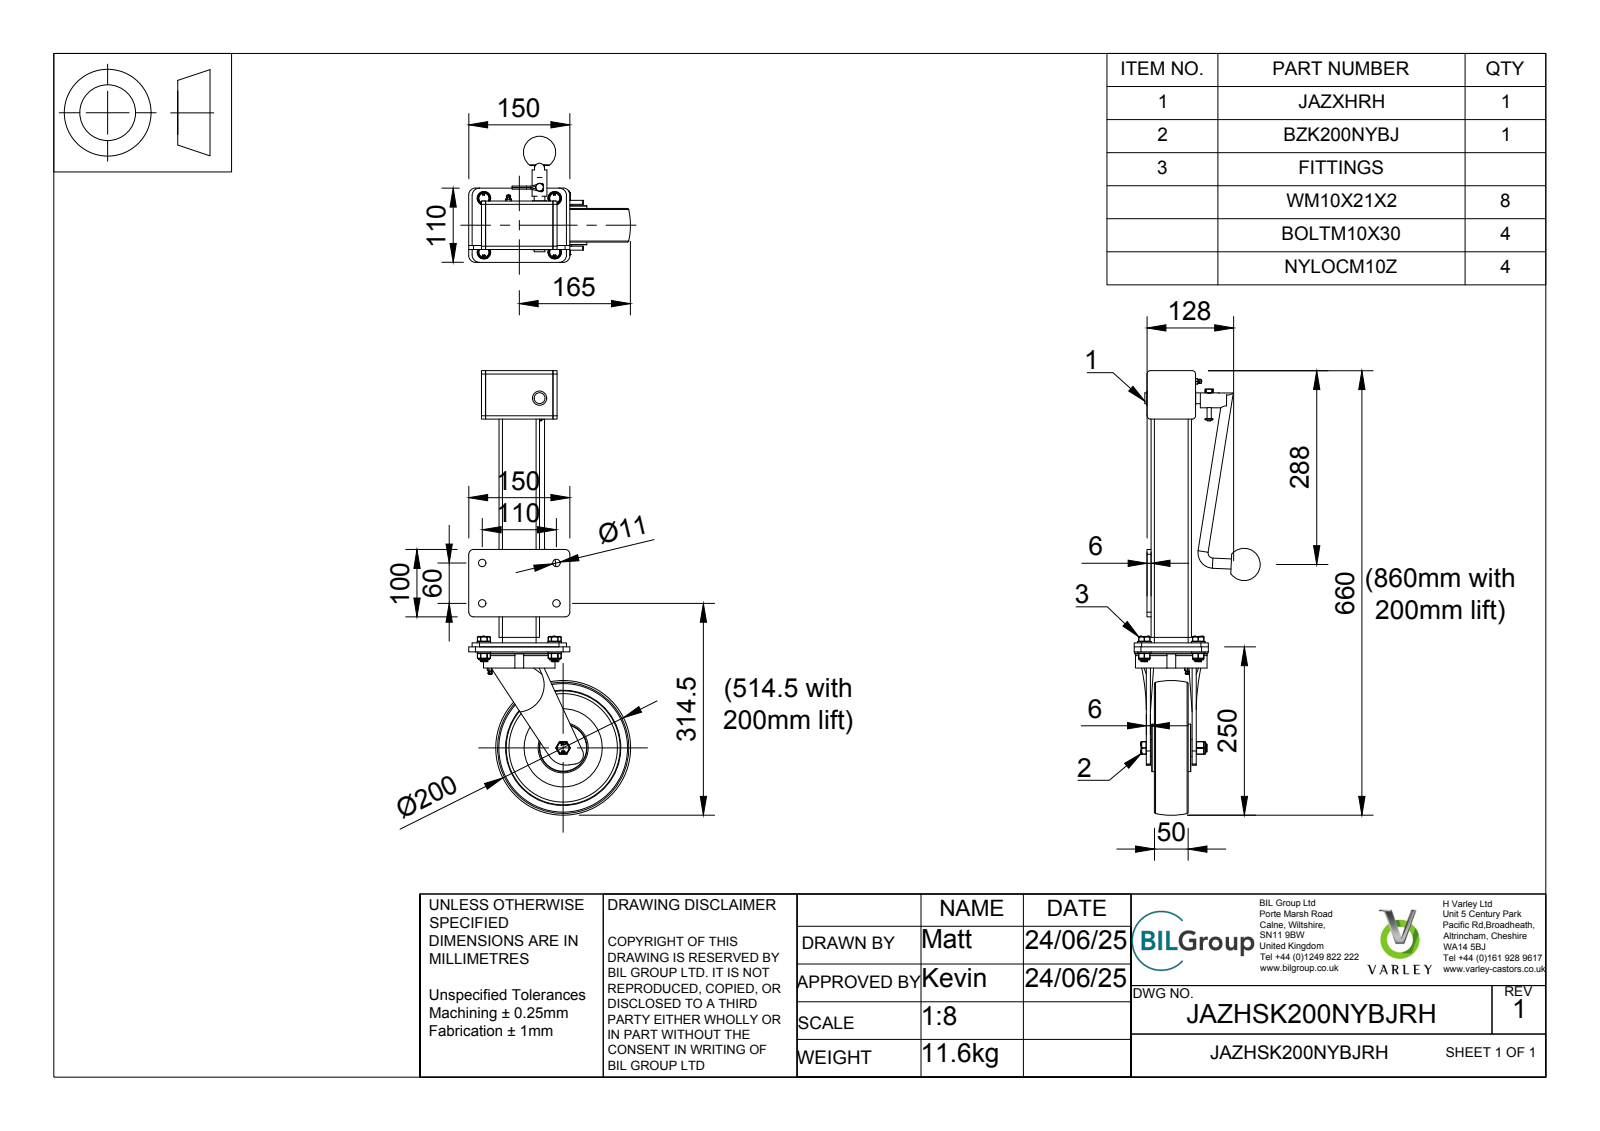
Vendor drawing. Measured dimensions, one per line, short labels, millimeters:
name: JAZHSK200NYBJRH v4; BZK200AS - 62 v1; FABRICATED STEEL FORKS; FABRICATED STEEL FORKS Geometry (+8 more)
written by: Autodesk Translation Framework v14.10.0.0 (AUTOMOTIVE_DESIGN)
unit: mm
bodies: 68 solids, 2090 faces (799 planar, 626 cylindrical, 665 other)
size: 660 × 240 × 186.96
volume: 2 847 000 mm³; area: 698 533 mm²
holes: 5× ⌀12, 4× ⌀10, 4× ⌀10.5, 4× ⌀11, 1× ⌀3, 1× ⌀6.25, 1× ⌀6.75, 1× ⌀12.2, 1× ⌀13, 1× ⌀14, 1× ⌀15, 1× ⌀16
bosses: 10× ⌀2, 4× ⌀20, 4× ⌀16, 4× ⌀9.85, 4× ⌀8.14, 1× ⌀108, 1× ⌀107, 1× ⌀70.5
rounds: 90× R0.5, 16× R0.33, 16× R0.64, 8× R0.63, 8× R0.64, 8× R4.84, 8× R5, 8× R5.33
face distances: 3.5, 6, 5, 1.5, 55, 51.5, 56.5, 50, 61, 62.5
hole spacings: 66, 60, 80, 105, 110, 125.3, 132, 3.22
